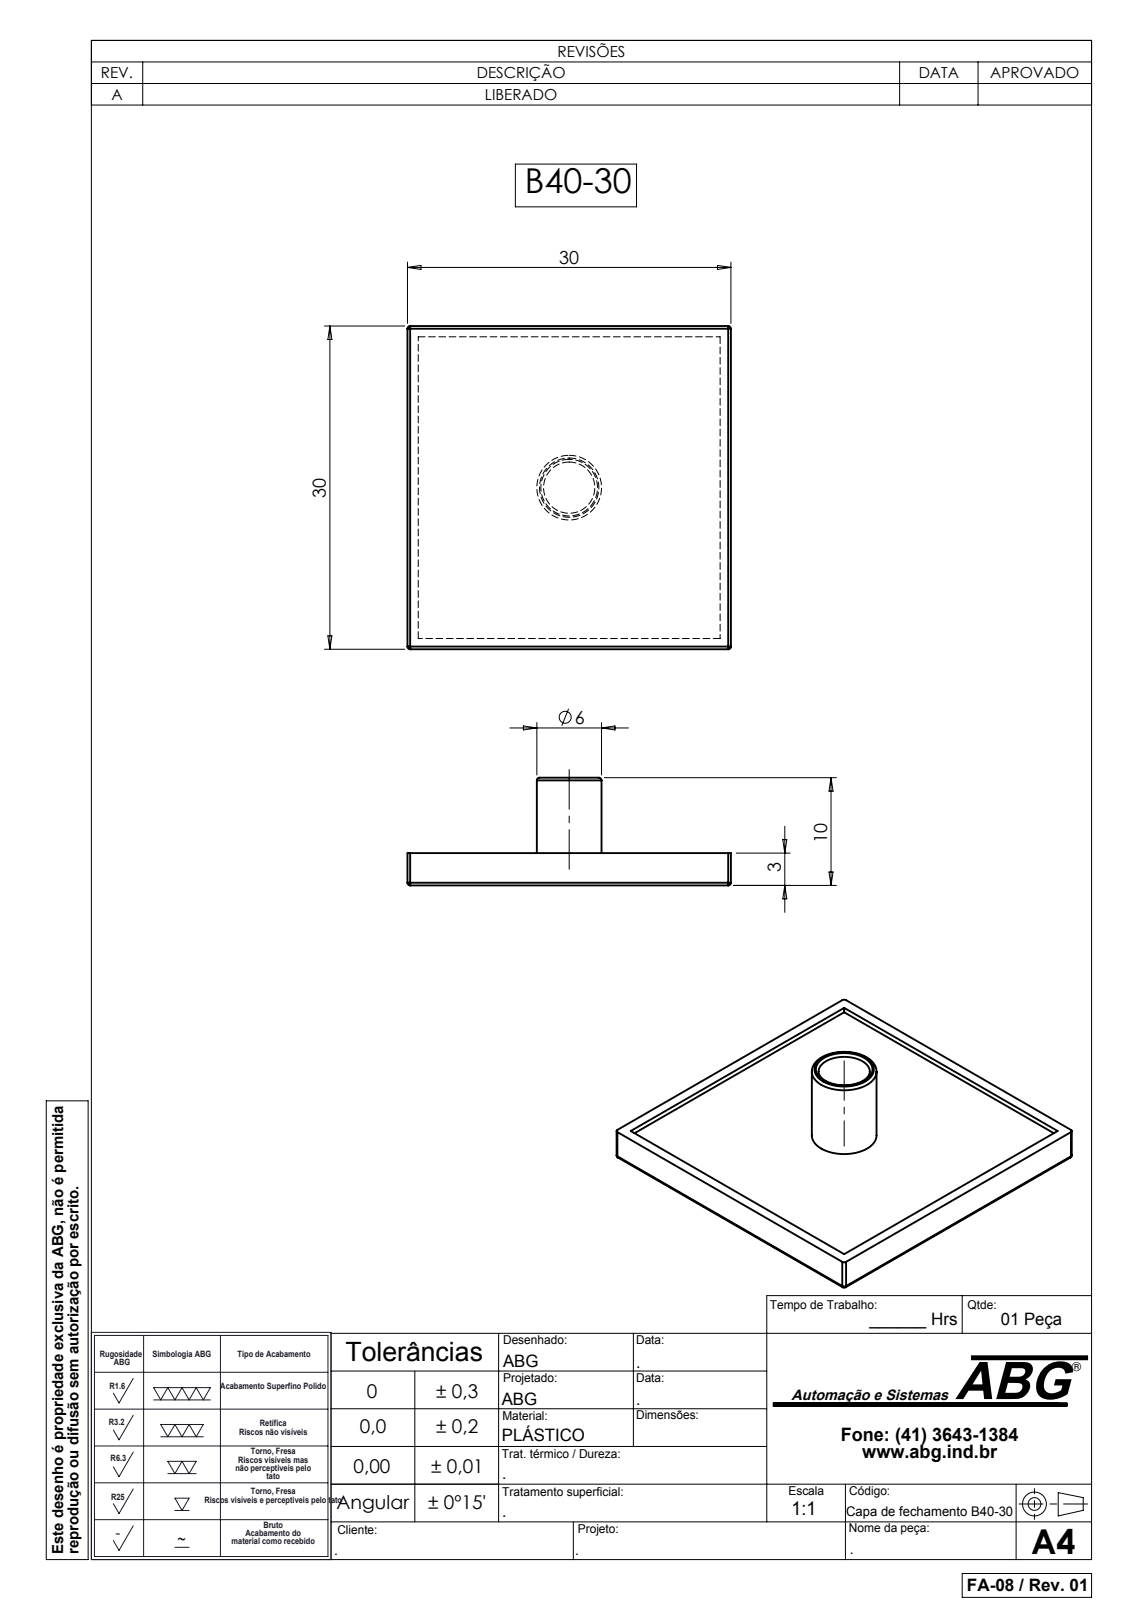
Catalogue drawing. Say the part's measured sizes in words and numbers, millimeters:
The part is named "B40-30". Its 3-D file was written by "SolidWorks 2007 (CONFIG_CONTROL_DESIGN)". It is 1 solid with 33 faces: 13 planar, 12 cylindrical and 8 other. Overall it measures 30 by 30 by 9 millimeters. Its volume is 1 494 cubic millimeters and its surface area 2 324 square millimeters. Round holes: 1 of diameter 4.75. Round bosses or shafts: 1 of diameter 6. Partial cylindrical surfaces (rounded edges, fillets, slot ends): 8 of radius 0.25. The main face-to-face distances are 1.5, 2, 0.5, 30, 1, 29, 28, 9, 7.5, 7.
